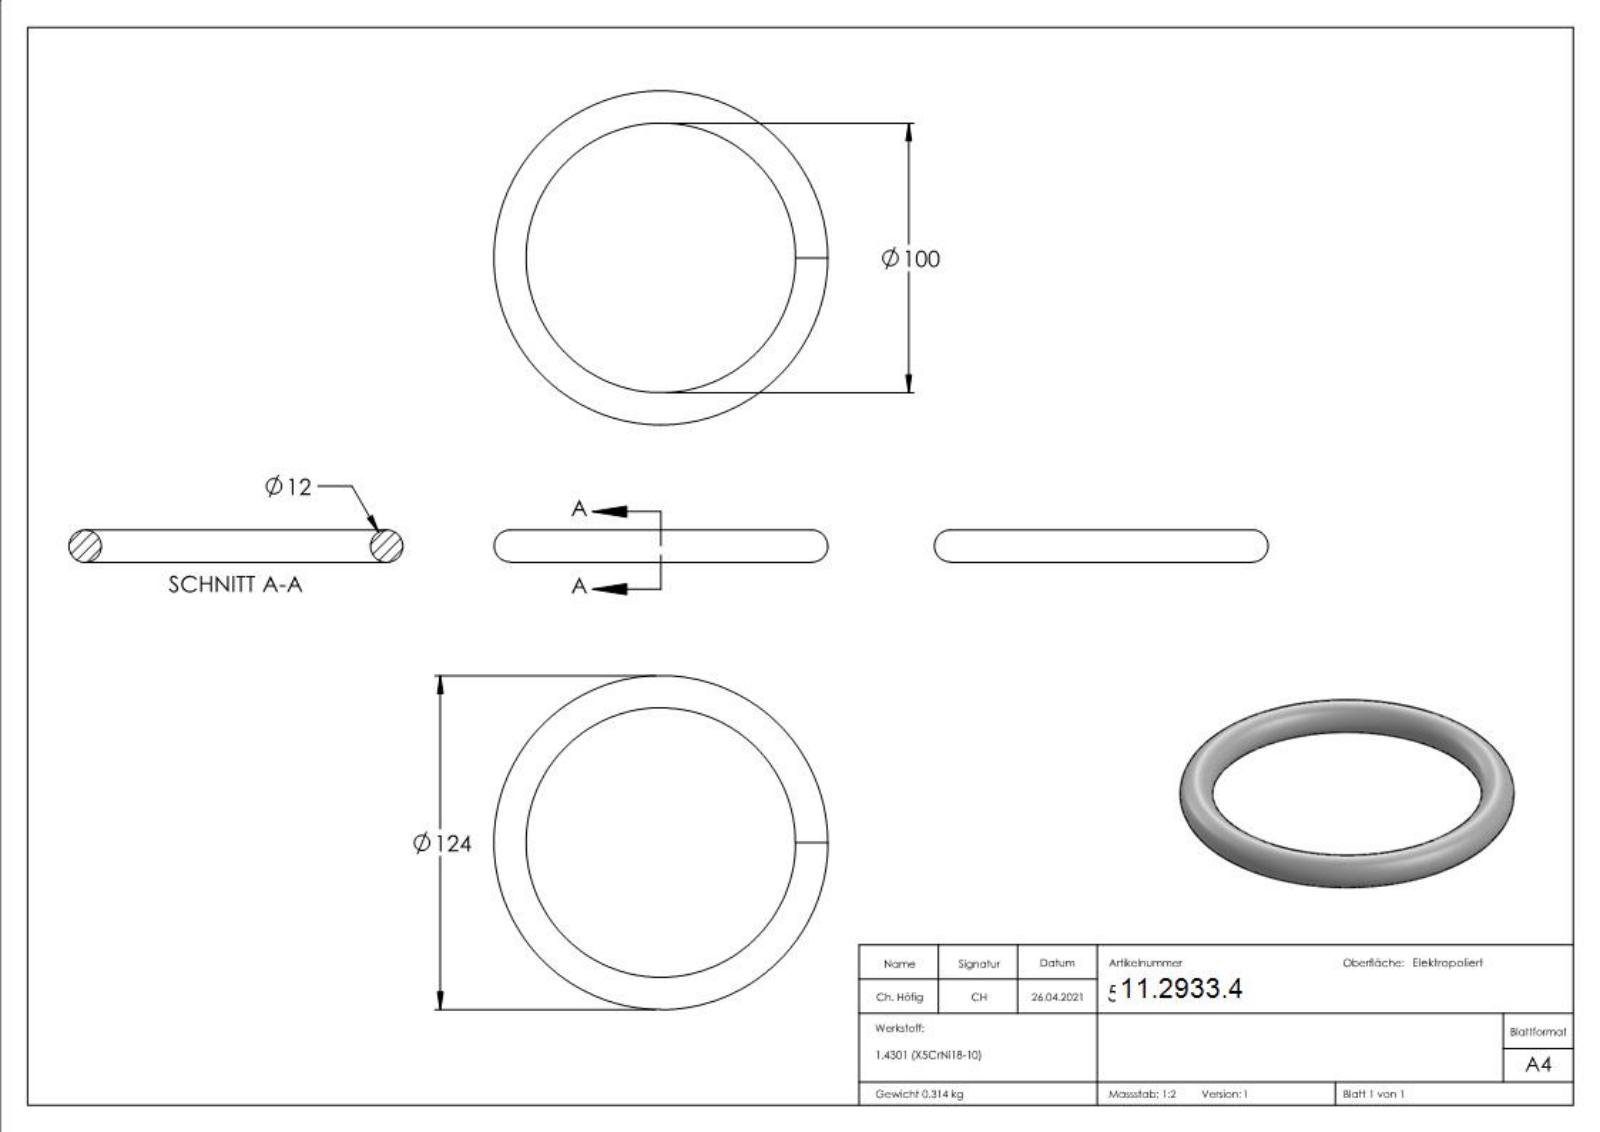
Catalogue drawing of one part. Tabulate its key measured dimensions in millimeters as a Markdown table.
| quantity | value |
| --- | --- |
| part name | 50381-240 |
| STEP written by | SolidWorks 2018 (CONFIG_CONTROL_DESIGN) |
| units | millimeters |
| bodies | 1 solid, 4 faces (0 planar, 0 cylindrical, 4 other) |
| overall size | 124 × 124 × 12 |
| volume | 39 794 mm³ |
| surface area | 13 265 mm² |
